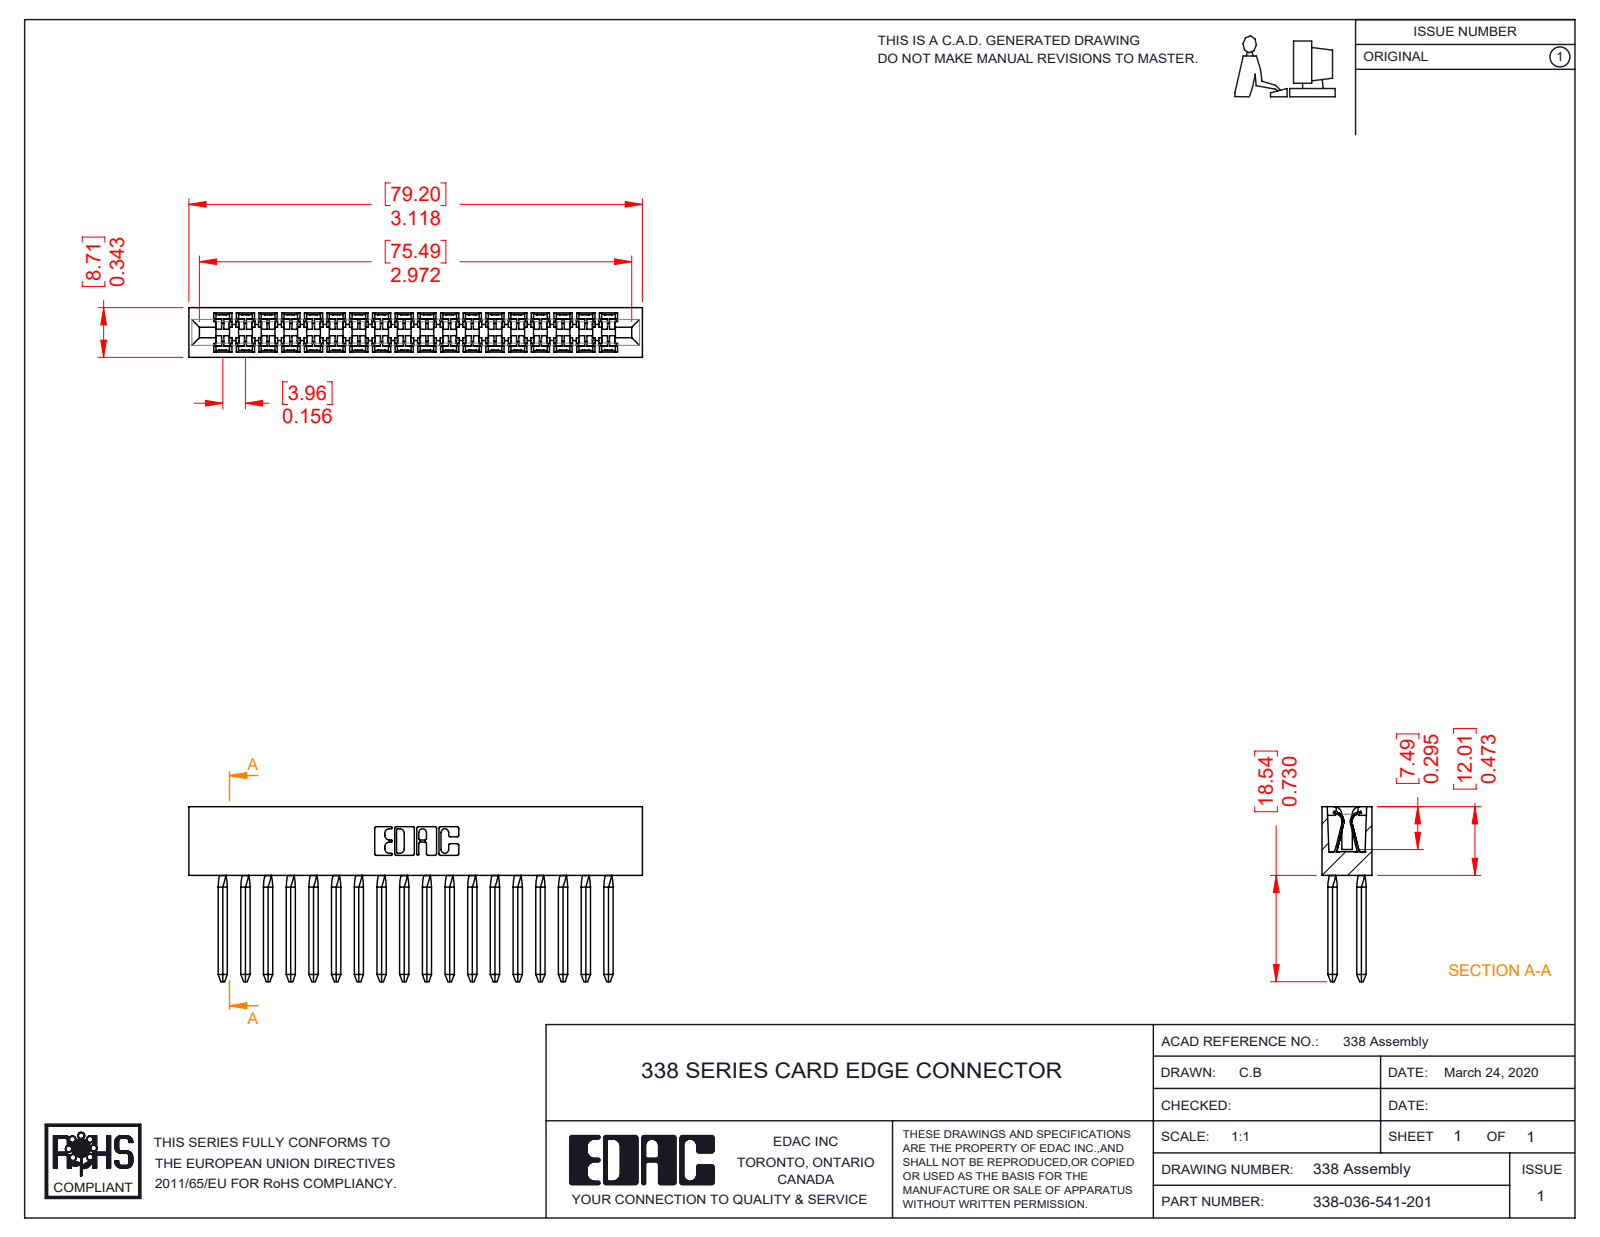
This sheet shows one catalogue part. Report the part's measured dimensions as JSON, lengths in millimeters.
{"part_name": "338-036-541-201; 338-210-001_338-210-018-001; 338-290-001_541", "step_written_by": "SolidWorks 2016 (CONFIG_CONTROL_DESIGN)", "units": "millimeters", "bodies": {"solids": 37, "faces": 2498, "planar": 1738, "cylindrical": 616, "other": 144}, "overall_size": [79.2, 30.6, 8.7], "volume_mm3": 6440, "surface_area_mm2": 12210, "partial_cylinders_radius": [[0.6, 110], [0.2, 36], [1.4, 30], [1.7, 30], [2.5, 28], [0.3, 22], [0.2, 6], [0.8, 6]], "face_to_face_distances": [8.7, 4, 15.8, 19.8, 2.8, 11.9, 31.7, 7.9, 3.4, 5.3]}
